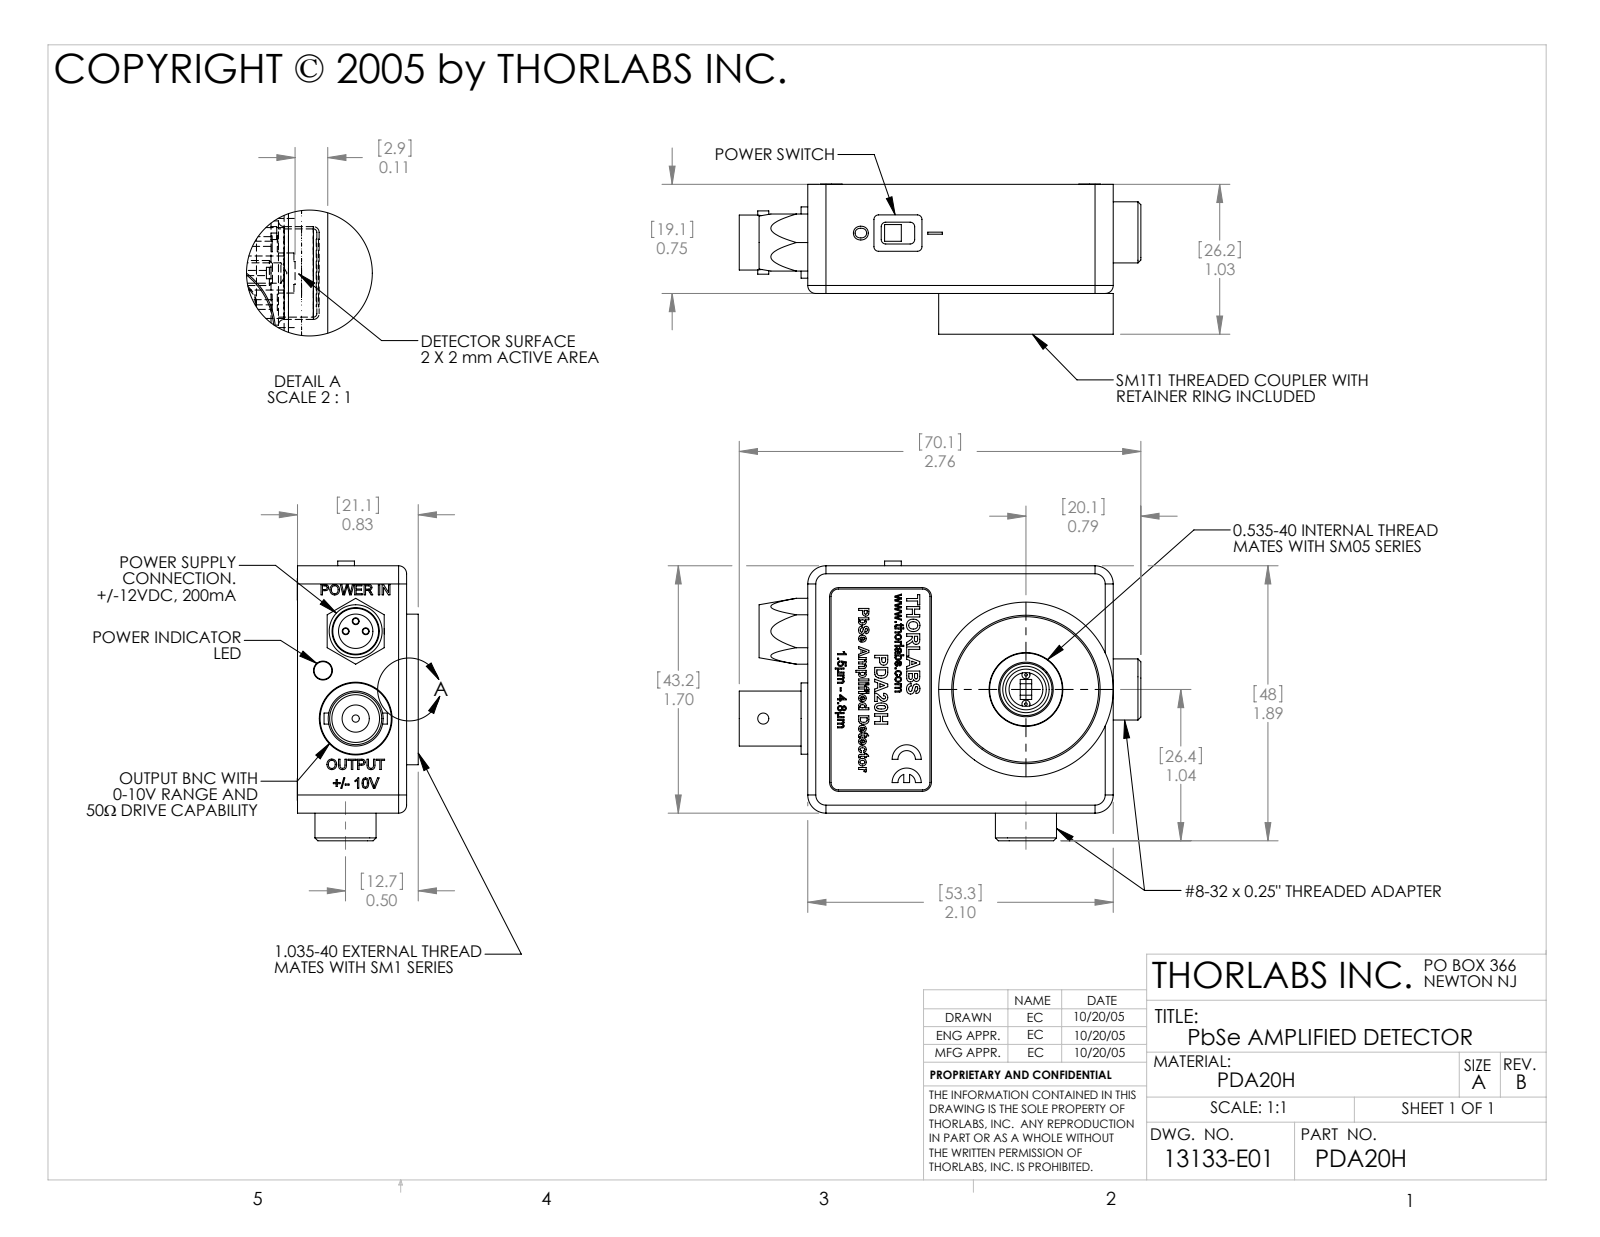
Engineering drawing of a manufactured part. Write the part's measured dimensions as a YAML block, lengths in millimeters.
part_name: "13133-E0W"
step_written_by: "SolidWorks 2009 (AUTOMOTIVE_DESIGN)"
units: millimeters
bodies: {solids: 17, faces: 1765, planar: 963, cylindrical: 269, other: 533}
overall_size: [70.13, 48.83, 26.2]
volume: 23732
surface_area: 26791
round_holes:
  - {diameter: 1.78, count: 7}
  - {diameter: 2.44, count: 7}
  - {diameter: 3.17, count: 4}
  - {diameter: 5.08, count: 4}
  - {diameter: 0.71, count: 3}
  - {diameter: 1, count: 3}
  - {diameter: 1.4, count: 2}
  - {diameter: 3.45, count: 2}
  - {diameter: 3.81, count: 2}
  - {diameter: 5, count: 2}
  - {diameter: 1.27, count: 1}
  - {diameter: 1.32, count: 1}
round_bosses_or_shafts:
  - {diameter: 3.73, count: 4}
  - {diameter: 2.18, count: 4}
  - {diameter: 0.45, count: 3}
  - {diameter: 10.67, count: 2}
  - {diameter: 5.99, count: 2}
  - {diameter: 30.48, count: 1}
  - {diameter: 26.29, count: 1}
  - {diameter: 12.7, count: 1}
partial_cylinders:
  - {radius: 3.17, count: 22}
  - {radius: 0.79, count: 12}
  - {radius: 2.41, count: 8}
  - {radius: 1.27, count: 4}
  - {radius: 1.4, count: 4}
  - {radius: 1.59, count: 4}
  - {radius: 0.25, count: 3}
  - {radius: 1.52, count: 2}
face_to_face_distances: [1.59, 2.54, 13.08, 11.49, 1.27, 11.48, 9.89, 1.6, 1.78, 4.19]
hole_center_spacings: [3.6, 22.16, 1.75, 2.54, 37.1, 2.47, 2.55, 3.59]
